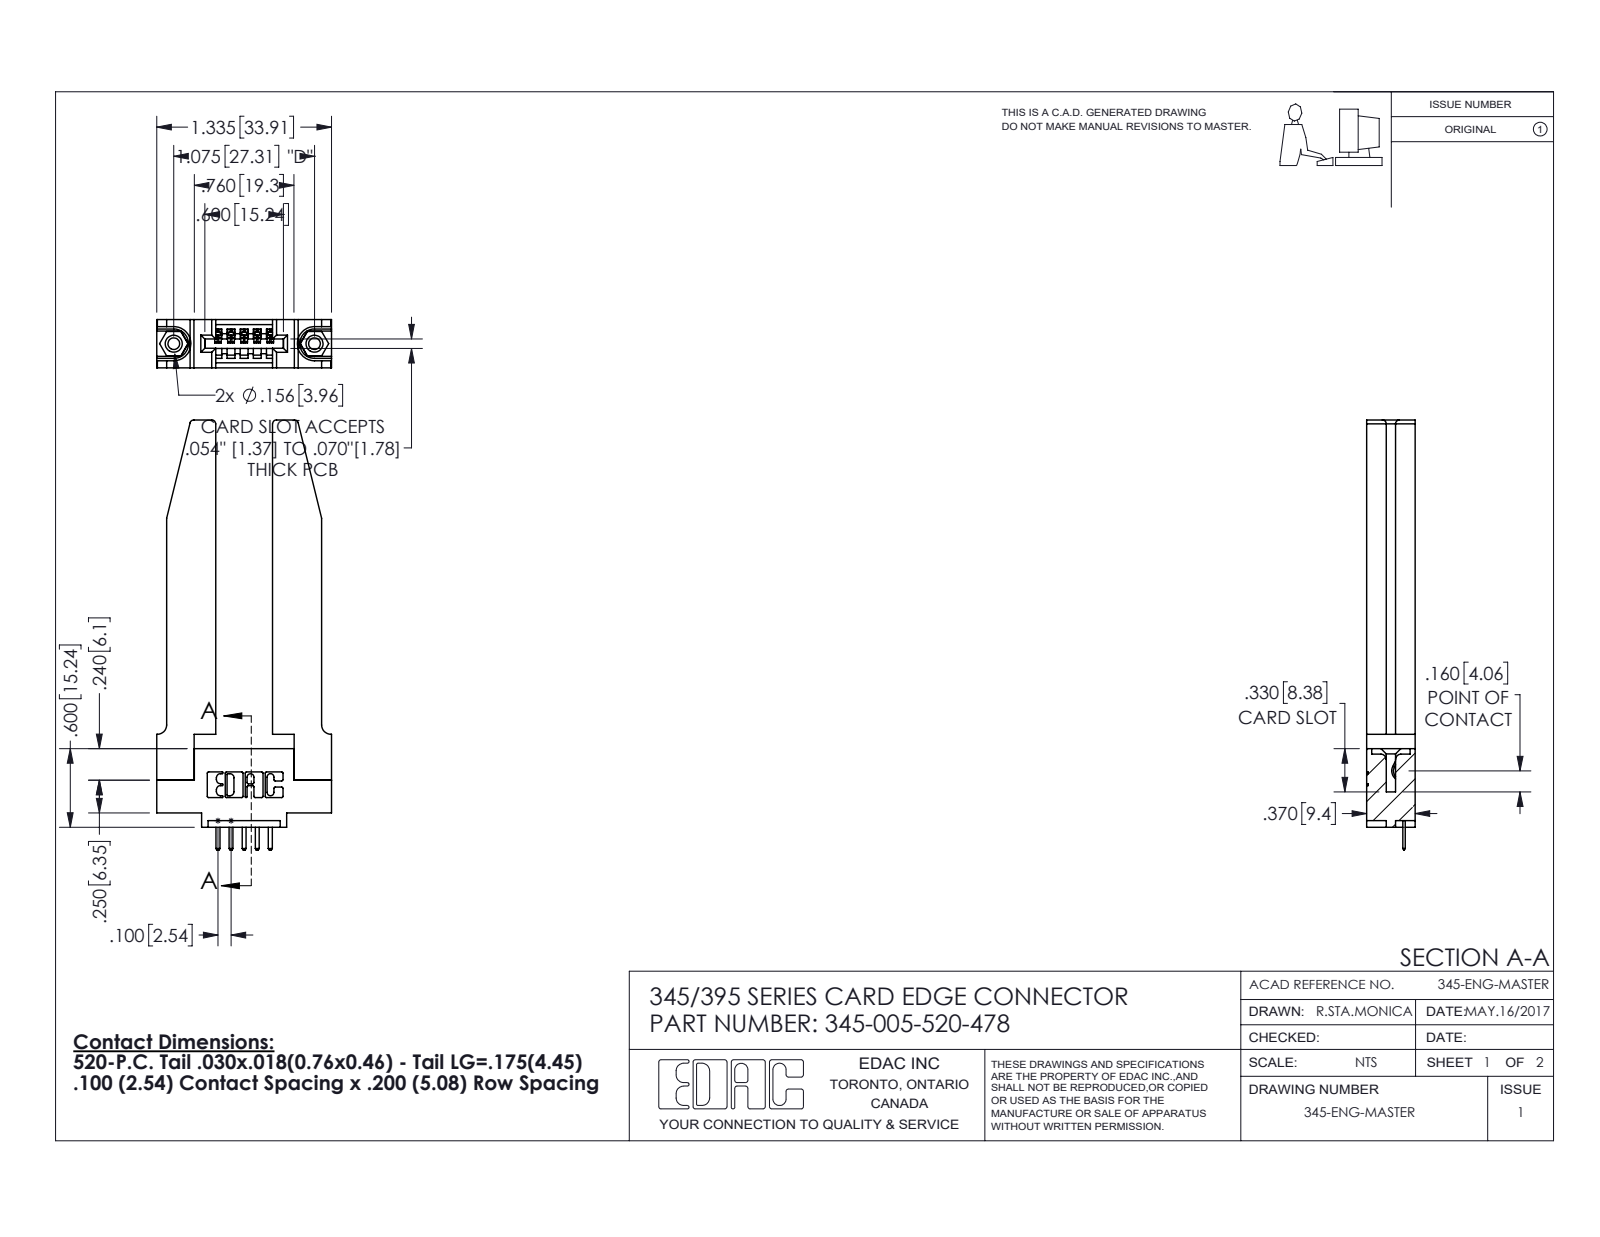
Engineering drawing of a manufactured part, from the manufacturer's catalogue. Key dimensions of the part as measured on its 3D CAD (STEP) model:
Part name (STEP PRODUCT): 345-250-001_345-250-001-102; 345-292-001_345-293-120; 345 Part_0.110 Offset - 0.156 Dia-TH; 345-005-520-478 (+1 more)
STEP written by: SolidWorks 2016 (CONFIG_CONTROL_DESIGN)
Units: inches
Bodies: 10 solids, 674 faces (436 planar, 186 cylindrical, 52 other)
Overall size (bounding box): 3.285 × 1.336 × 0.37
Volume: 0.647 in³ · Surface area: 15.72 in²
Round holes (diameter × count): ⌀0.089 ×2, ⌀0.125 ×2, ⌀0.156 ×2, ⌀0.064 ×1
Round bosses / shafts (diameter × count): ⌀0.155 ×2
Partial cylindrical surfaces — rounded edges, fillets, slot ends (radius × count): R0.01 ×22, R0.01 ×12, R0.006 ×10, R0.03 ×8, R0.007 ×6, R0.031 ×6, R0.026 ×3, R0.031 ×2
Main face-to-face distances: 0.37, 0.15, 0.22, 0.435, 0.072, 0.148, 0.298, 0.077, 0.071, 0.055
Hole centre spacings: 0.27, 0.847, 1.075
